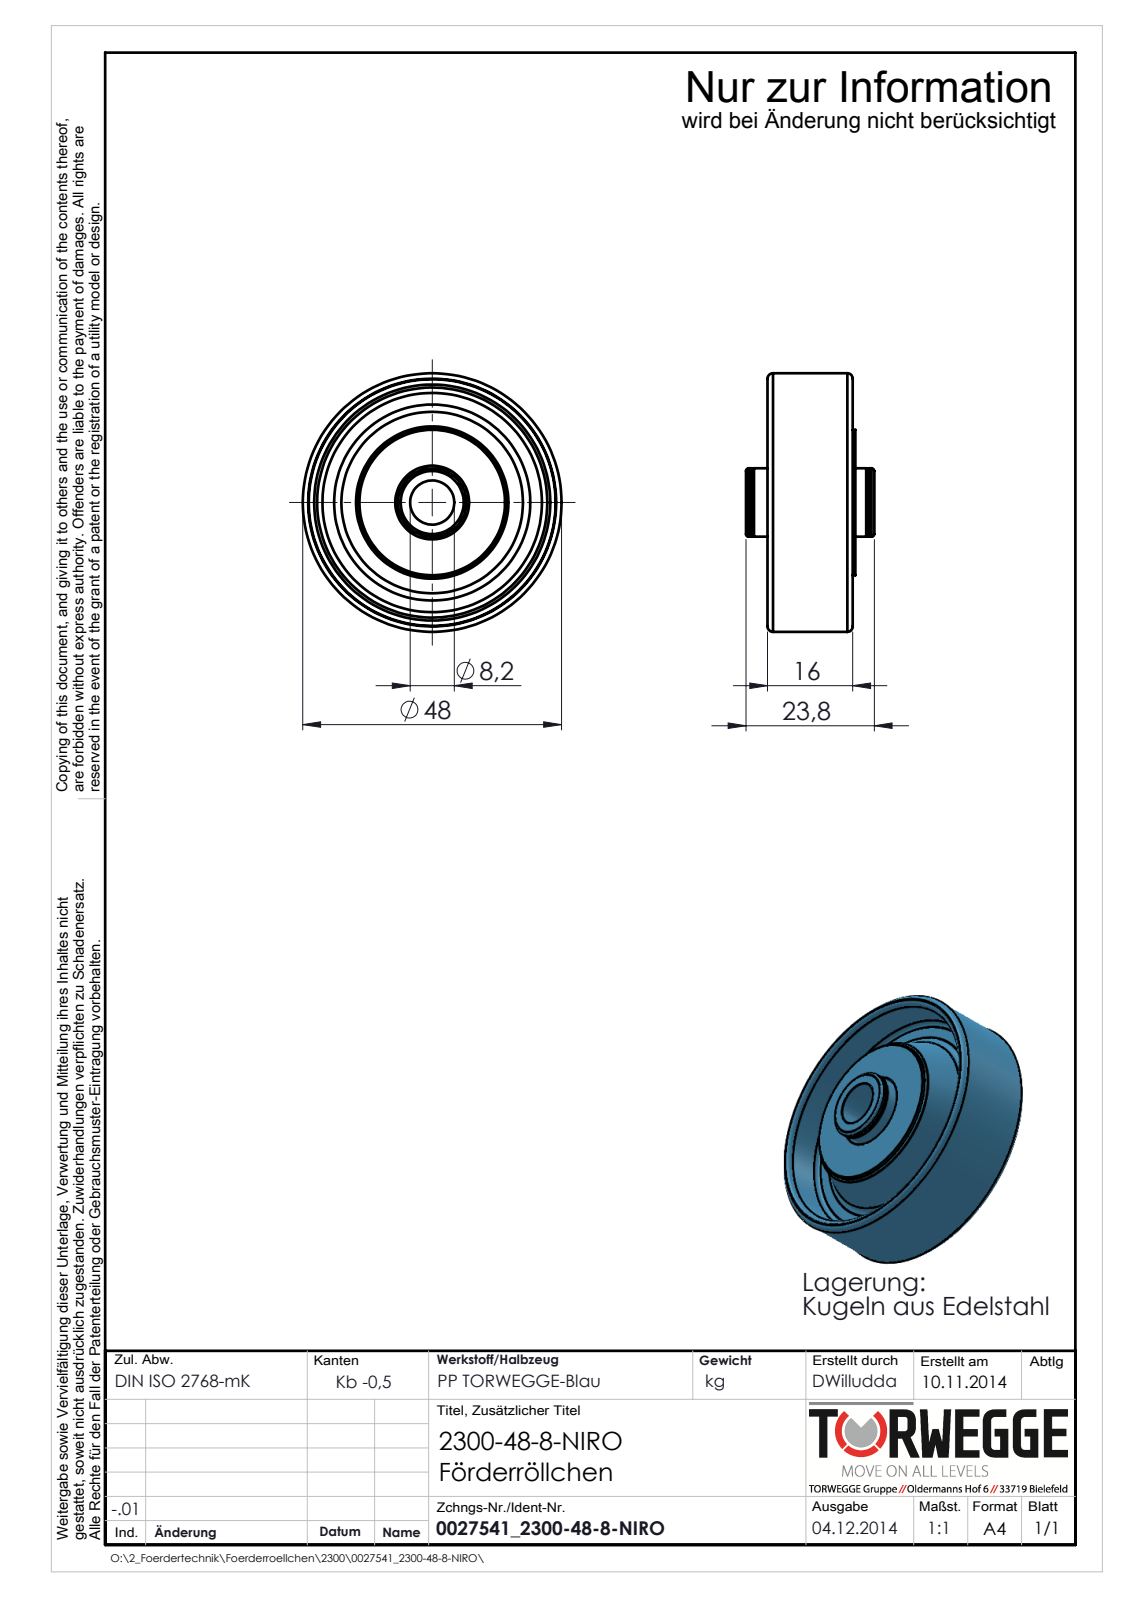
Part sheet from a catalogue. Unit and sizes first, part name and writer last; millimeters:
Units: millimetres
Overall size (bounding box): 48 × 48 × 23.8
Round holes (diameter × count): ⌀8.2 ×1, ⌀13.7 ×1
Round bosses / shafts (diameter × count): ⌀48 ×1, ⌀27 ×1, ⌀12.7 ×1
Main face-to-face distances: 16.3, 9.05, 6.75, 7.25, 2.3, 9.55, 10.75, 13.05, 4, 3.5
Volume: 18 913 mm³ · Surface area: 9 568 mm²
Bodies: 1 solid, 69 faces (11 planar, 18 cylindrical, 40 other)
Part name (STEP PRODUCT): 0027541_2300-48-8-NIRO
STEP written by: SolidWorks 2016 (AUTOMOTIVE_DESIGN)
